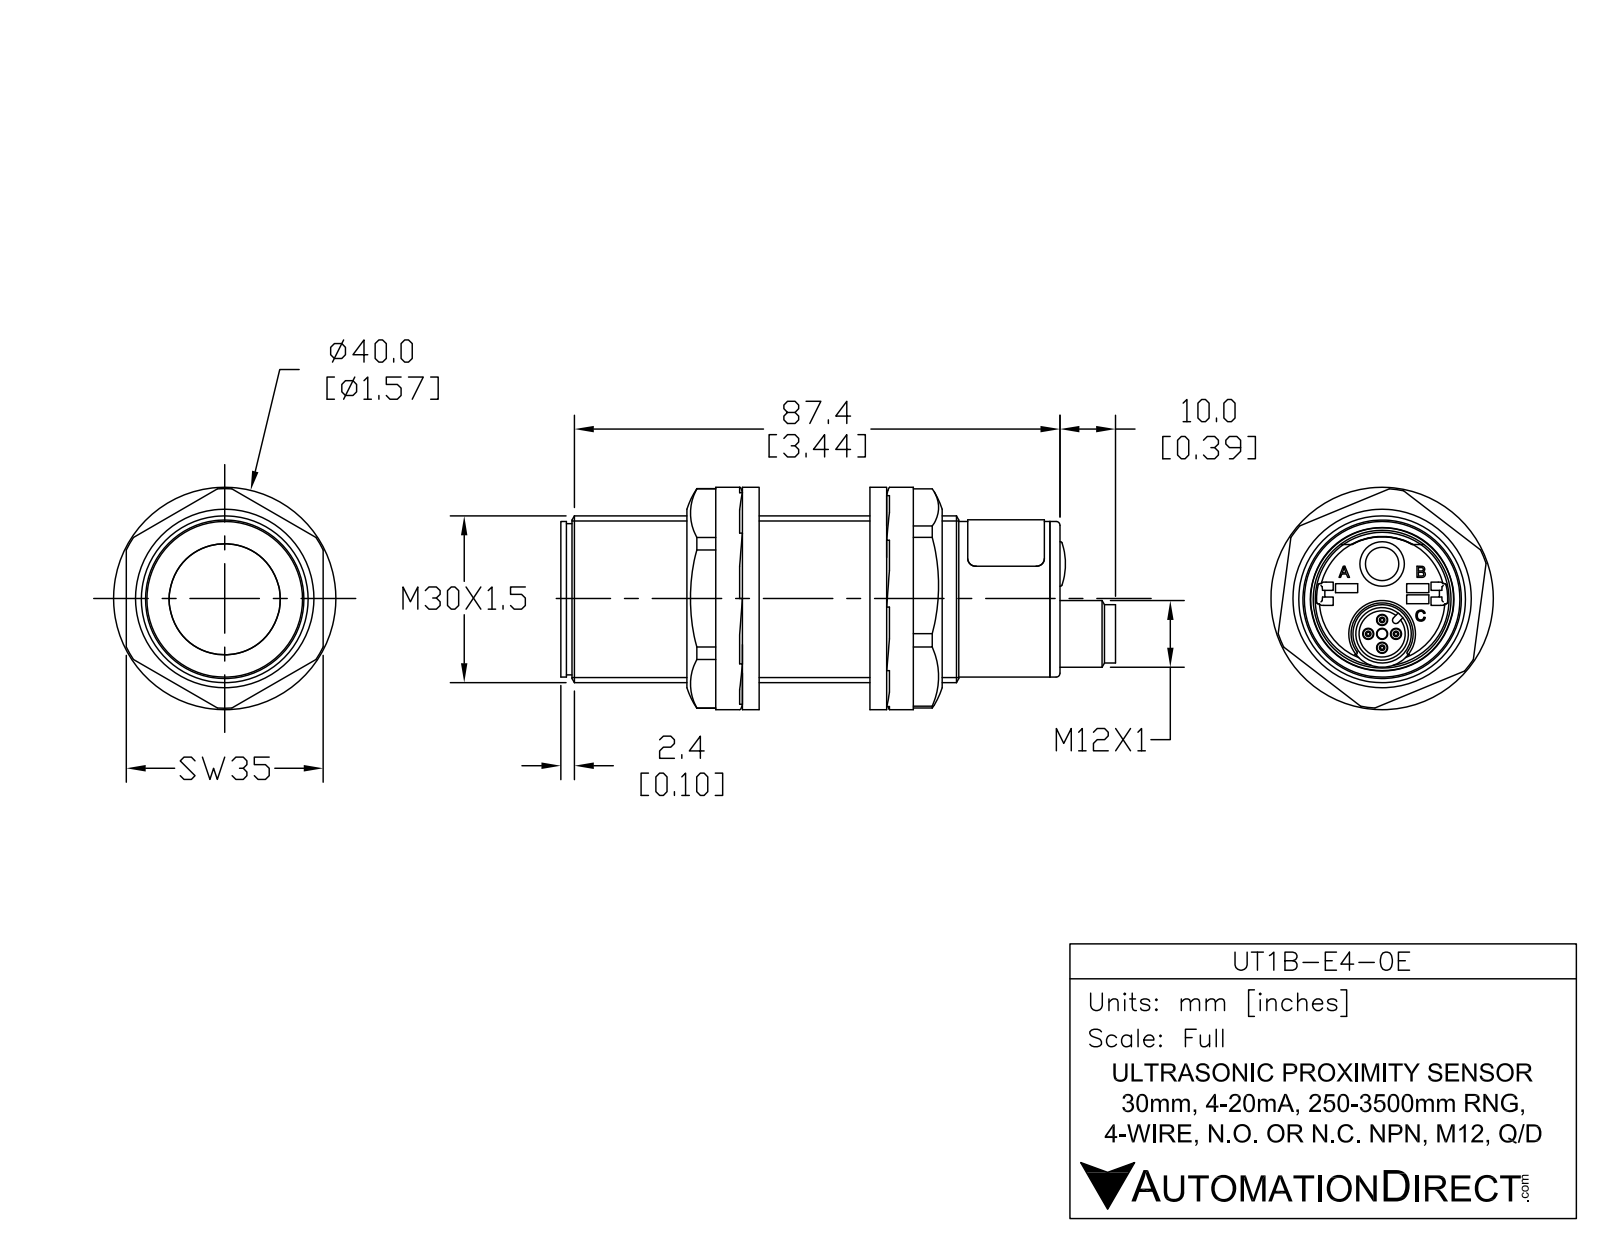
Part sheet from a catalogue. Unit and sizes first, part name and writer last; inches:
Units: inches
Overall size (bounding box): 3.89 × 1.181 × 1.181
Round holes (diameter × count): ⌀0.071 ×4, ⌀0.315 ×1, ⌀0.327 ×1, ⌀0.372 ×1, ⌀0.925 ×1
Round bosses / shafts (diameter × count): ⌀0.039 ×4, ⌀1.181 ×1, ⌀1.102 ×1, ⌀1.071 ×1, ⌀0.472 ×1, ⌀0.413 ×1, ⌀0.364 ×1
Partial cylindrical surfaces — rounded edges, fillets, slot ends (radius × count): R0.012 ×2, R0.024 ×1
Main face-to-face distances: 3.386, 3.457, 0.039, 3.425, 0.071, 3.496, 0.039, 0.059, 3.425, 3.496
Hole centre spacings: 0.098, 0.139, 0.197, 0.264, 0.505, 0.146, 0.245, 0.25
Volume: 3.754 in³ · Surface area: 20.71 in²
Bodies: 5 solids, 107 faces (30 planar, 45 cylindrical, 32 other)
Part name (STEP PRODUCT): UT1B-E4-0E
STEP written by: SolidWorks 2017 (AUTOMOTIVE_DESIGN)
